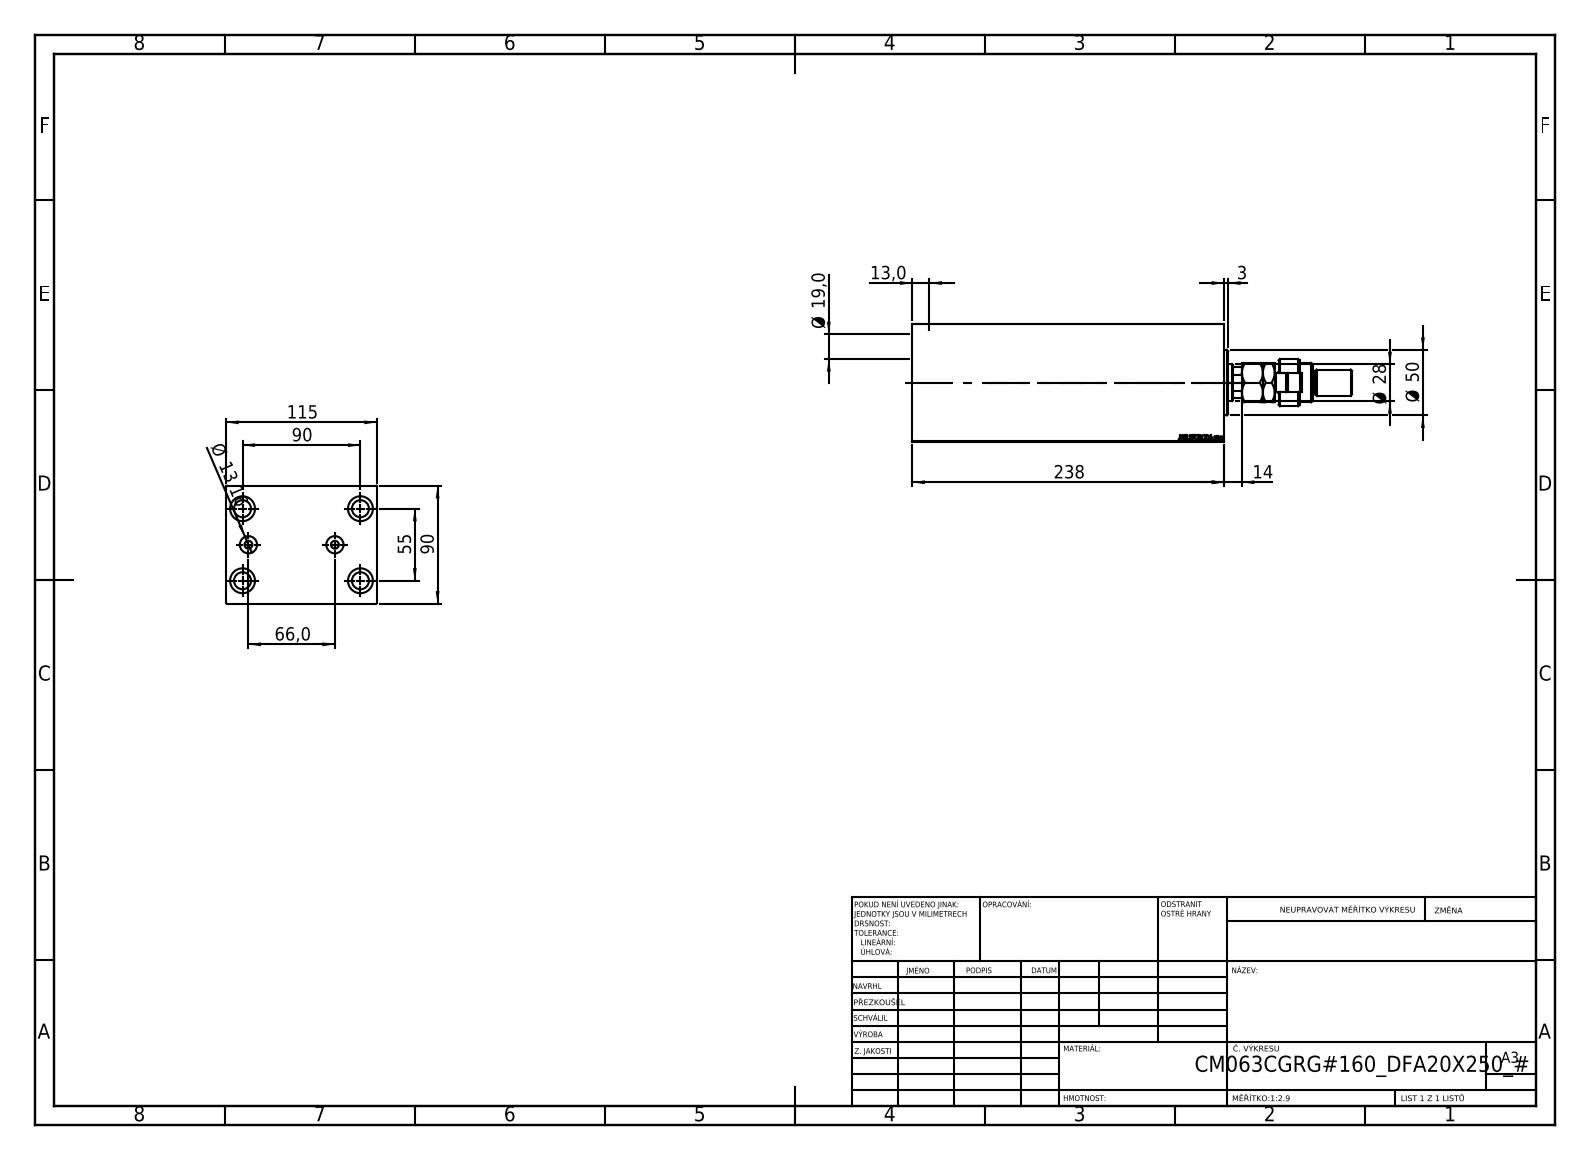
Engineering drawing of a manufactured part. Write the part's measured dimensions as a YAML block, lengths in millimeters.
part_name: "V450CM_VC_B; V450CM_C_Body; MFA; FEMALE_PART_FOR_DFA (+1 more)"
step_written_by: "SolidWorks 2019 (CONFIG_CONTROL_DESIGN)"
units: millimeters
bodies: {solids: 5, faces: 945, planar: 436, cylindrical: 71, other: 438}
overall_size: [335.5, 115, 90]
volume: 1965000
surface_area: 265023
round_holes:
  - {diameter: 13, count: 4}
  - {diameter: 19, count: 4}
  - {diameter: 6, count: 2}
  - {diameter: 13.16, count: 2}
  - {diameter: 18.5, count: 1}
  - {diameter: 28, count: 1}
  - {diameter: 31.5, count: 1}
  - {diameter: 63, count: 1}
  - {diameter: 65, count: 1}
  - {diameter: 72, count: 1}
round_bosses_or_shafts:
  - {diameter: 50, count: 1}
  - {diameter: 36, count: 1}
  - {diameter: 30, count: 1}
  - {diameter: 22, count: 1}
  - {diameter: 20, count: 1}
  - {diameter: 18, count: 1}
  - {diameter: 14, count: 1}
partial_cylinders:
  - {radius: 7.5, count: 1}
  - {radius: 12, count: 1}
  - {radius: 13.5, count: 1}
face_to_face_distances: [90, 115, 238, 17.5, 220.5, 13.5, 207, 224.5, 64.5, 47]
hole_center_spacings: [52.74, 27.87, 33.71, 55, 75.67, 89.81, 90, 105.48]
